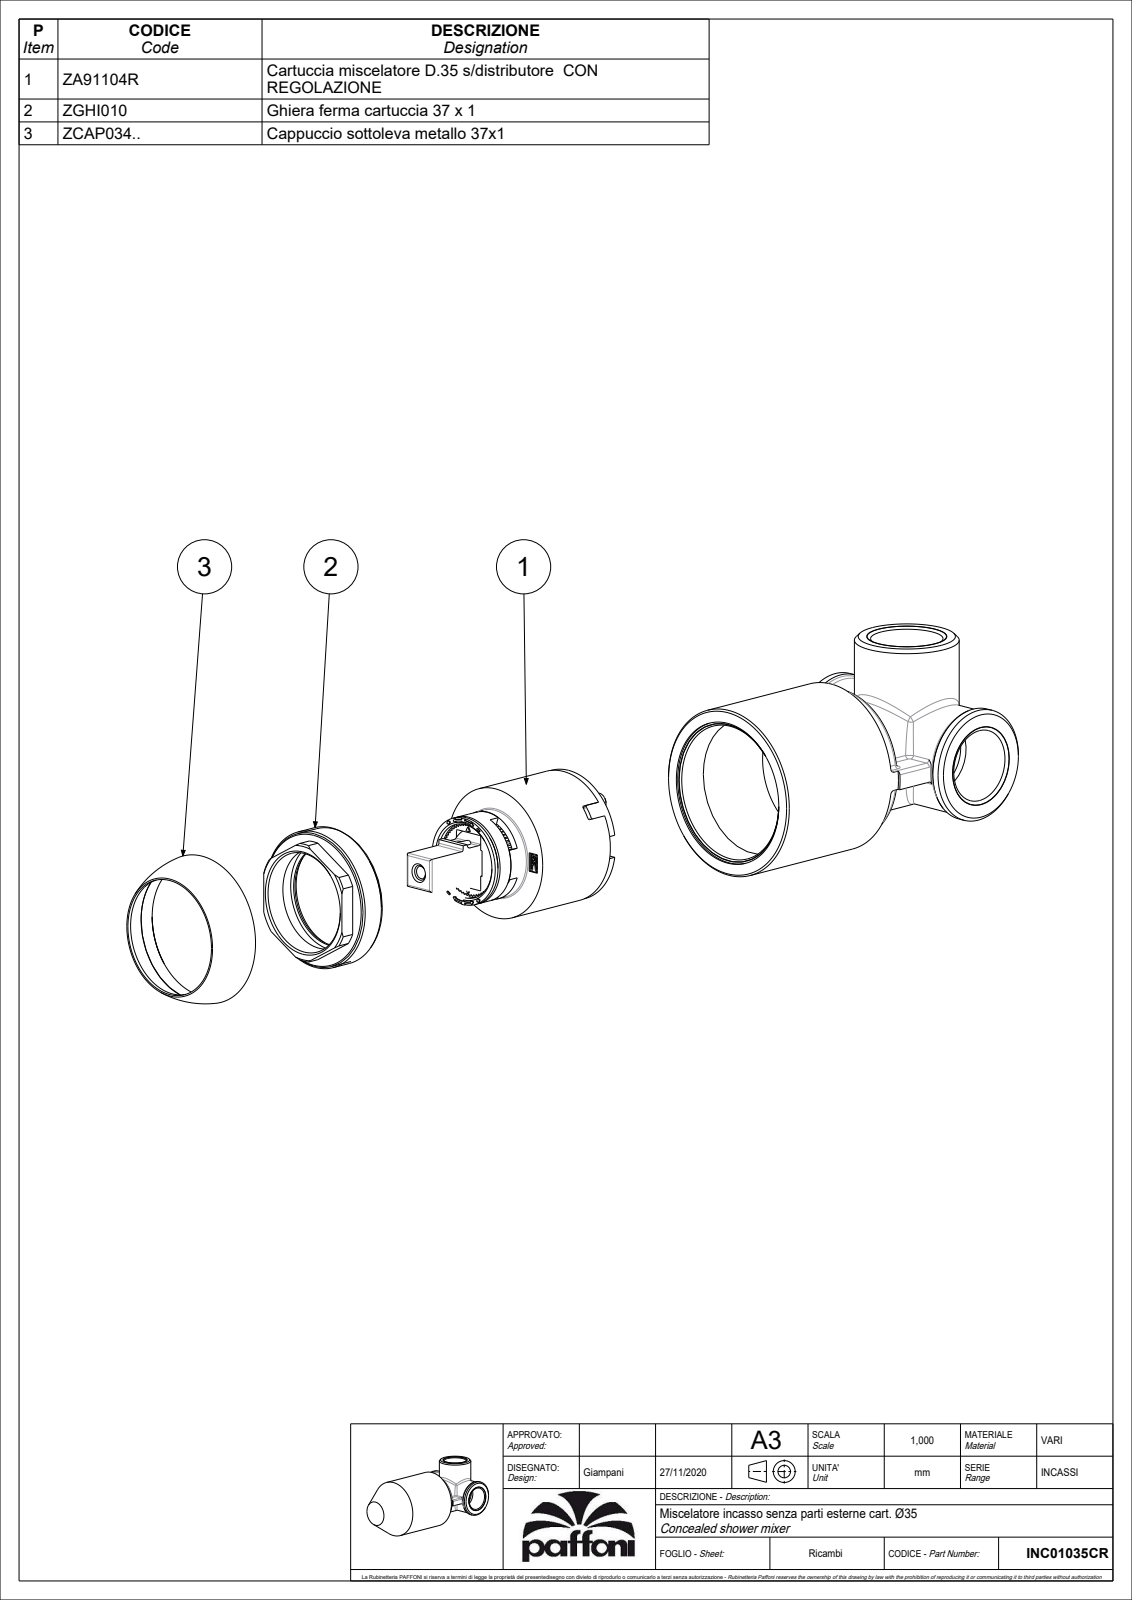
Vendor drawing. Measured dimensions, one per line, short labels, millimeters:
name: INC01035CR
written by: CREO PARAMETRIC BY PTC INC, 2020044 (CONFIG_CONTROL_DESIGN)
unit: mm
bodies: 2 solids, 982 faces (565 planar, 229 cylindrical, 188 other)
size: 113.4 × 55 × 54
volume: 97 246 mm³; area: 61 638 mm²
holes: 2× ⌀4, 2× ⌀7, 2× ⌀19, 1× ⌀3.3, 1× ⌀5, 1× ⌀8, 1× ⌀8.5, 1× ⌀16, 1× ⌀19.5, 1× ⌀19.9, 1× ⌀26.8, 1× ⌀29
bosses: 1× ⌀48, 1× ⌀44.8, 1× ⌀40, 1× ⌀35, 1× ⌀34.8, 1× ⌀32.2, 1× ⌀30, 1× ⌀29.8
rounds: 27× R0.5, 18× R1, 11× R0.15, 4× R0.3, 1× R7, 1× R9.3, 1× R10.85, 1× R11.25
face distances: 32, 5.5, 38, 10, 1.5, 37.5, 6, 2, 4, 0.5
hole spacings: 8.6, 12, 4.75, 14, 68.1, 74.6
